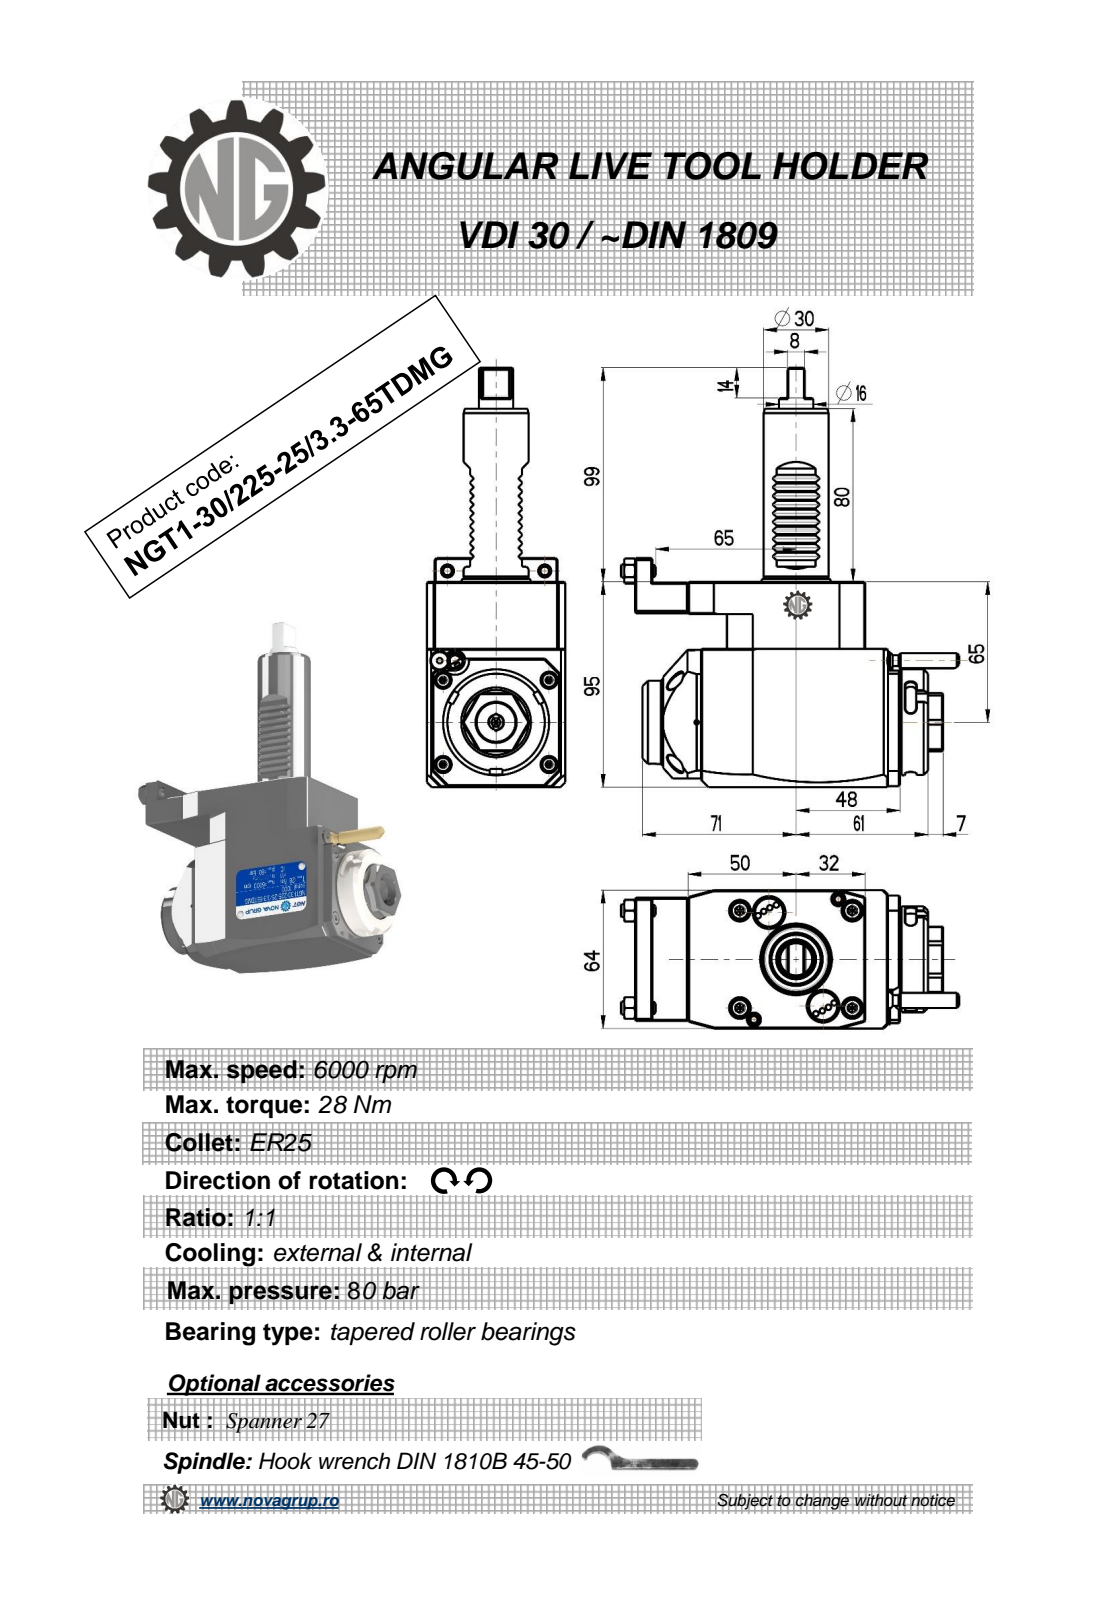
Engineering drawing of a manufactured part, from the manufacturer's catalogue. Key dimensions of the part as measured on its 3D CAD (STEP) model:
Part name (STEP PRODUCT): NGT1_30_225_25_3_3_65TDMG
STEP written by: PRO/ENGINEER BY PARAMETRIC TECHNOLOGY CORPORATION, 2010280 (CONFIG_CONTROL_DESIGN)
Units: millimetres
Bodies: 1 solid, 452 faces (238 planar, 100 cylindrical, 114 other)
Overall size (bounding box): 194 × 156.38 × 64
Volume: 660 266 mm³ · Surface area: 62 965 mm²
Round holes (diameter × count): ⌀2 ×2, ⌀2.6 ×2, ⌀2.5 ×1, ⌀3 ×1, ⌀18 ×1
Round bosses / shafts (diameter × count): ⌀6 ×2, ⌀49 ×1, ⌀42 ×1, ⌀40 ×1, ⌀38.5 ×1, ⌀30 ×1, ⌀15.9 ×1, ⌀8 ×1
Partial cylindrical surfaces — rounded edges, fillets, slot ends (radius × count): R0.3 ×20, R0.31 ×10, R0.2 ×6, R2.5 ×6, R0.8 ×2, R180 ×2, R4.5 ×1, R15 ×1
Main face-to-face distances: 64, 95, 16, 0.5, 80, 14.5, 16.5, 80.5, 3.5, 13
Hole centre spacings: 14.25, 28.5, 28.89, 34.25, 43.79
